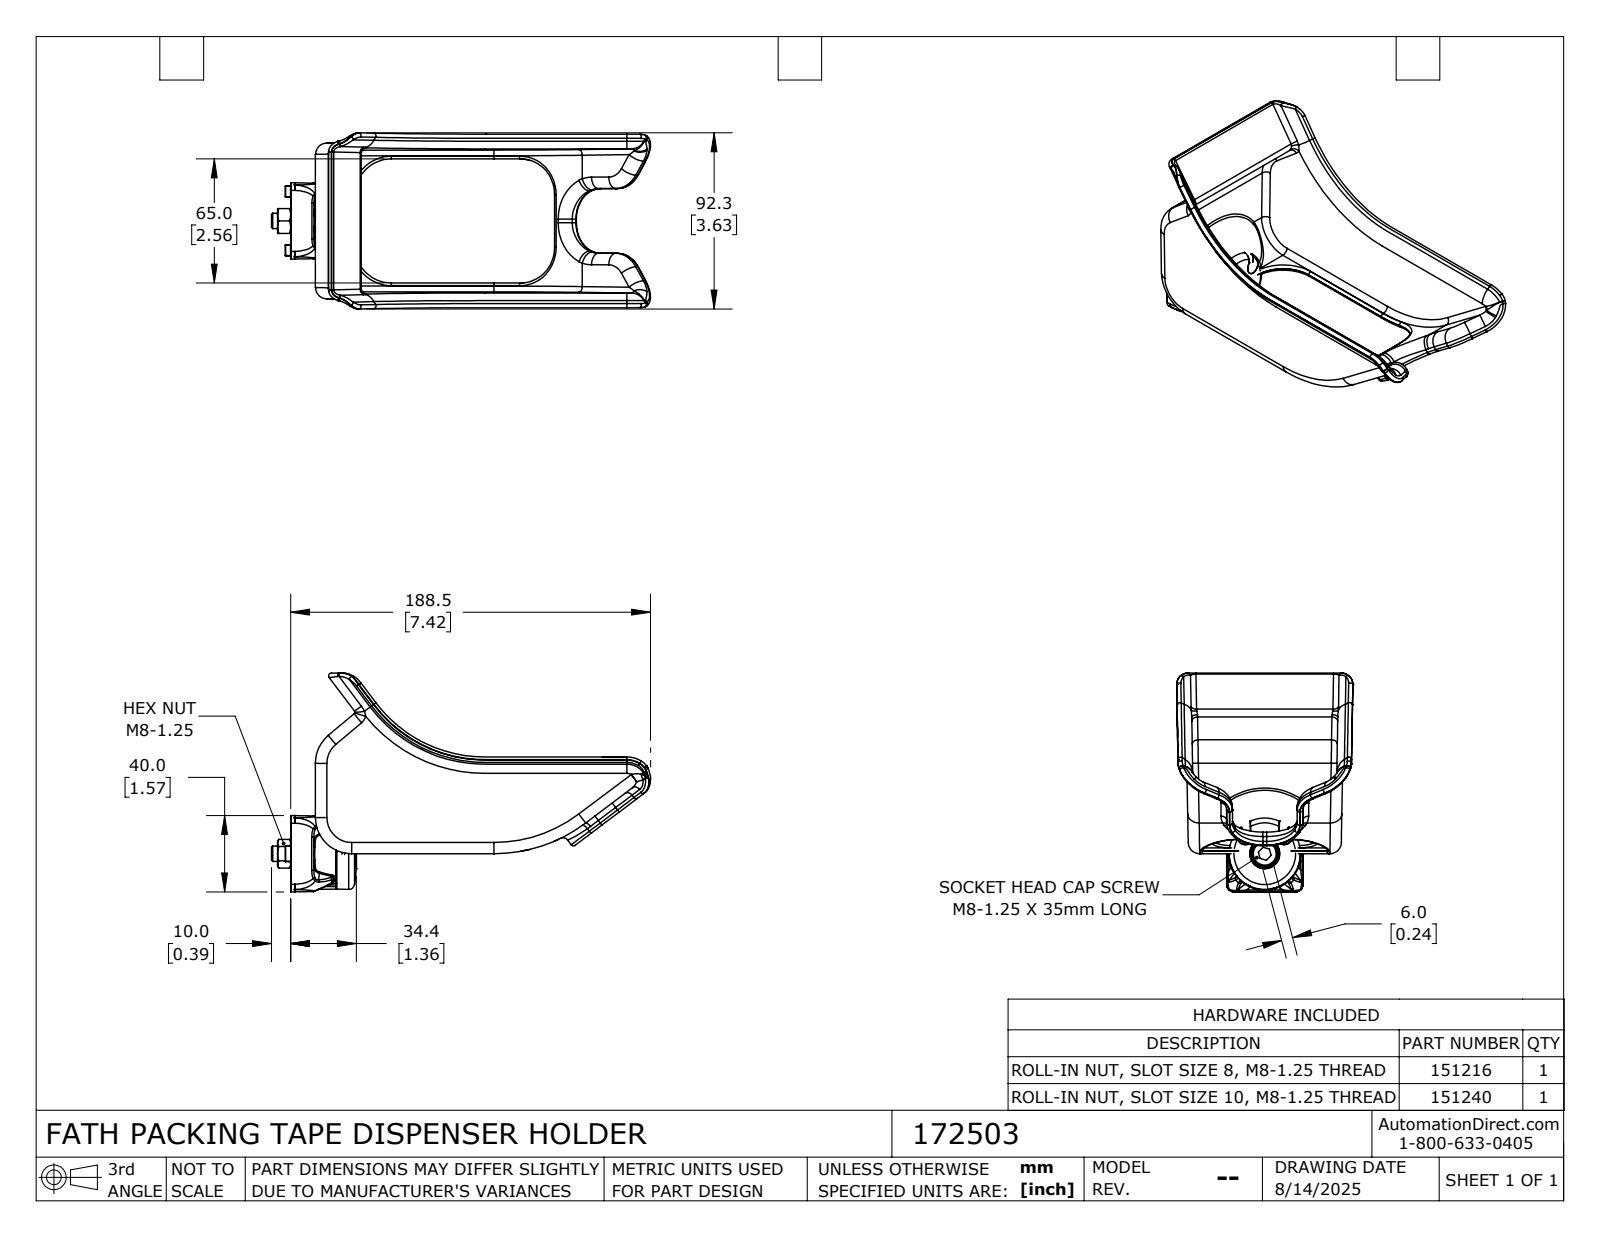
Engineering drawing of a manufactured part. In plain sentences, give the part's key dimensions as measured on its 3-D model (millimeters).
The part is named "172503". Its 3-D file was written by "SolidWorks 2024 (CONFIG_CONTROL_DESIGN)". It is 7 solids with 2221 faces: 340 planar, 528 cylindrical and 1353 other. Overall it measures 198.54 by 114.6 by 92.29 millimeters. Its volume is 141 494 cubic millimeters and its surface area 85 781 square millimeters. Round holes: 1 of diameter 6.8, 1 of diameter 8, 1 of diameter 13.01. Round bosses or shafts: 1 of diameter 31, 1 of diameter 13. Partial cylindrical surfaces (rounded edges, fillets, slot ends): 178 of radius 0.2, 122 of radius 0.5, 17 of radius 6, 16 of radius 1.4, 16 of radius 3, 9 of radius 1, 8 of radius 1.45, 8 of radius 4. The main face-to-face distances are 3, 13, 8, 16, 2.99, 6, 13.5, 2.5, 11, 0.5.
